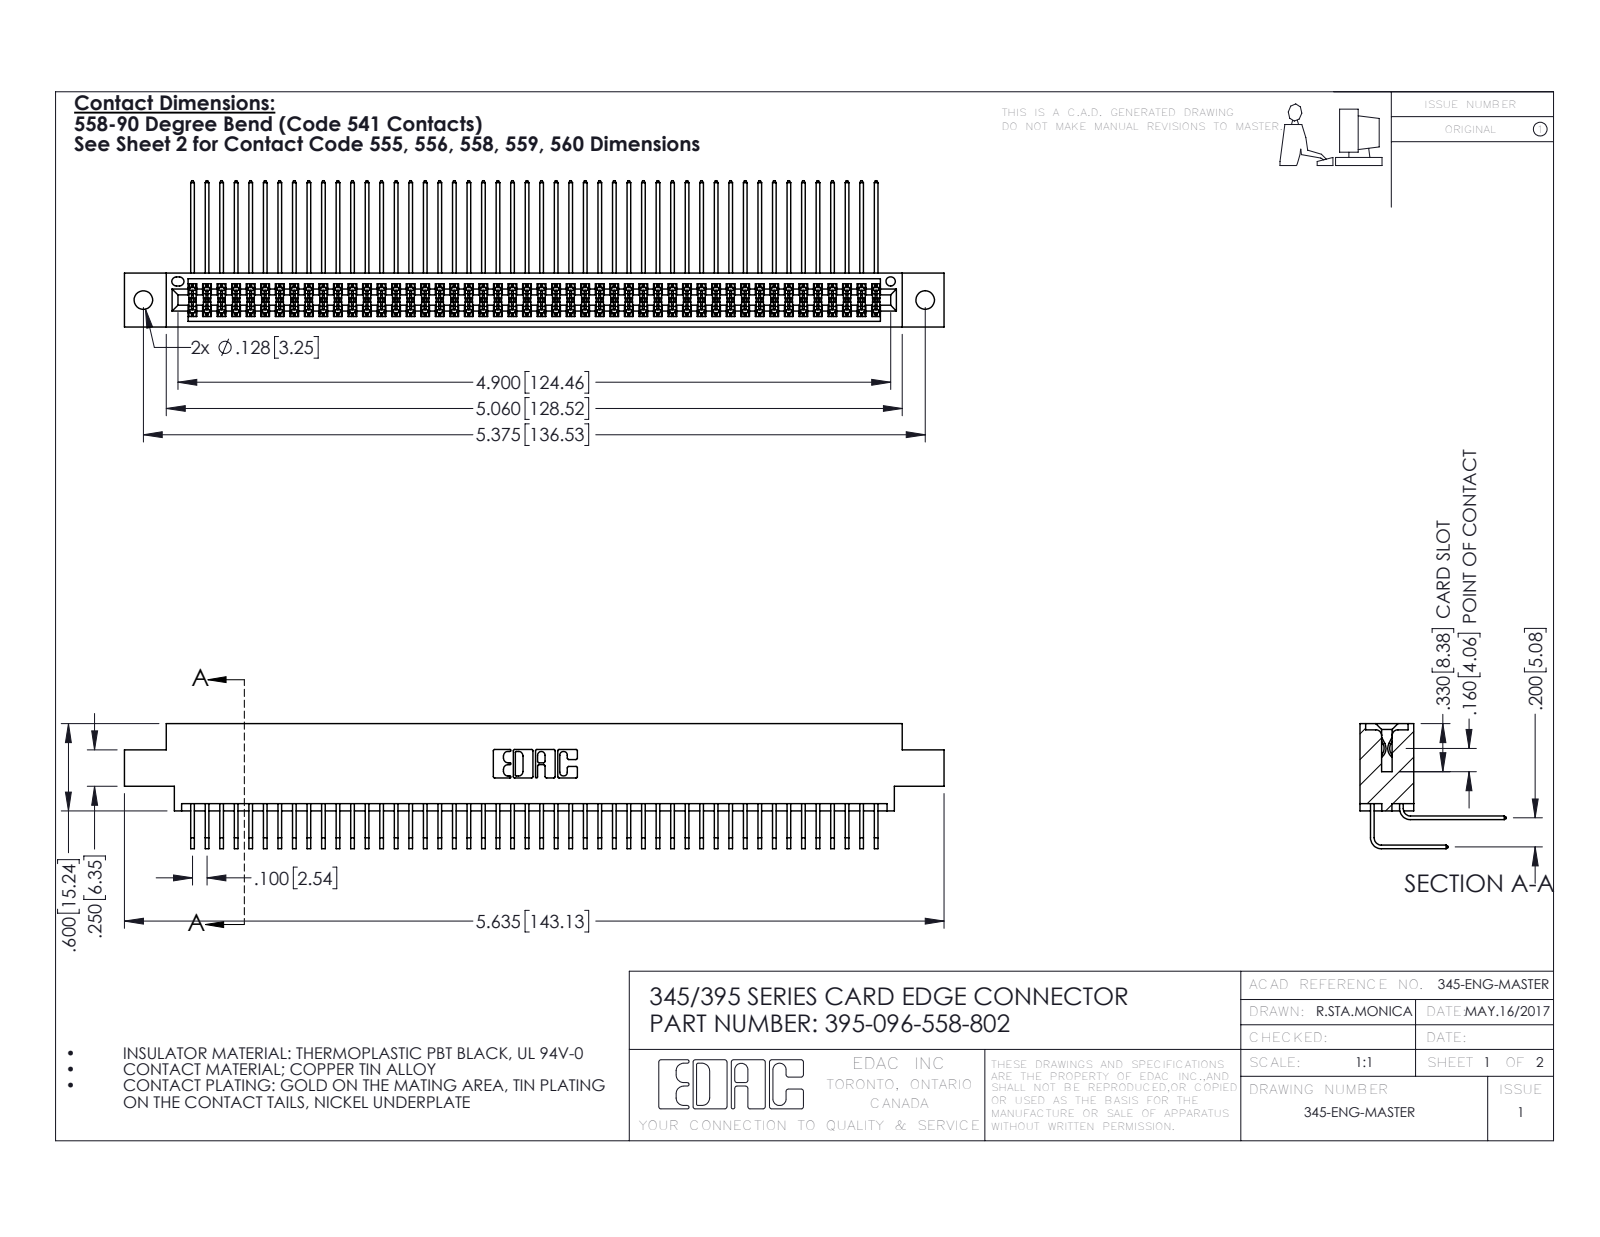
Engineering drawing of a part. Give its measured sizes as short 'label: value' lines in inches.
name: 395-096-558-802; 345 Part_0.170 Offset - 0.128 Dia; 345-292-001_558 Tail - 2; 345-292-001_558 559 Tail - 1
written by: SolidWorks 2016 (CONFIG_CONTROL_DESIGN)
unit: in
bodies: 97 solids, 5122 faces (3444 planar, 1678 cylindrical, 0 other)
size: 5.635 × 1.005 × 0.859
volume: 0.876 in³; area: 36.92 in²
holes: 2× ⌀0.128, 1× ⌀0.064
rounds: 144× R0.006, 22× R0.01, 6× R0.007, 6× R0.031, 3× R0.026, 2× R0.014, 2× R0.019, 2× R0.022
face distances: 0.072, 0.298, 0.2, 0.37, 0.098, 0.272, 0.025, 0.225, 0.175, 0.025
hole spacings: 0.27, 5.139, 5.375
